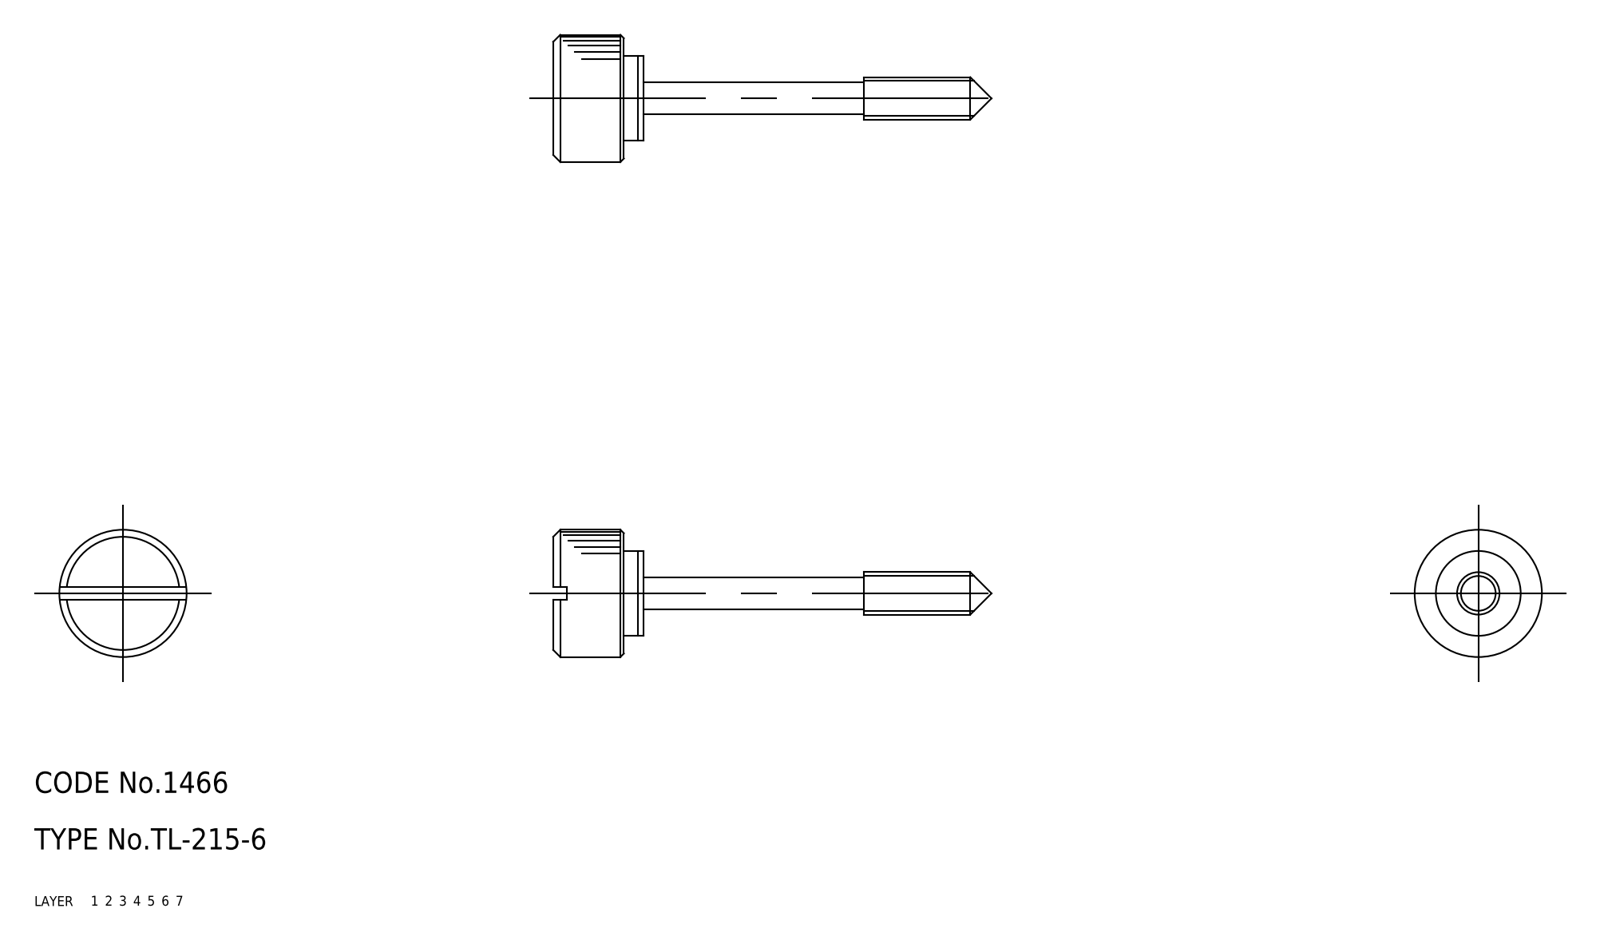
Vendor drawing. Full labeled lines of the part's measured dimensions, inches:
Part name (STEP PRODUCT): washer; knob; TL_215_6_26021_36
STEP written by: CADfix (AUTOMOTIVE_DESIGN)
Units: inches
Bodies: 2 solids, 42 faces (0 planar, 0 cylindrical, 42 other)
Overall size (bounding box): 2.441 × 0.709 × 0.709
Volume: 0.227 in³ · Surface area: 3.336 in²
